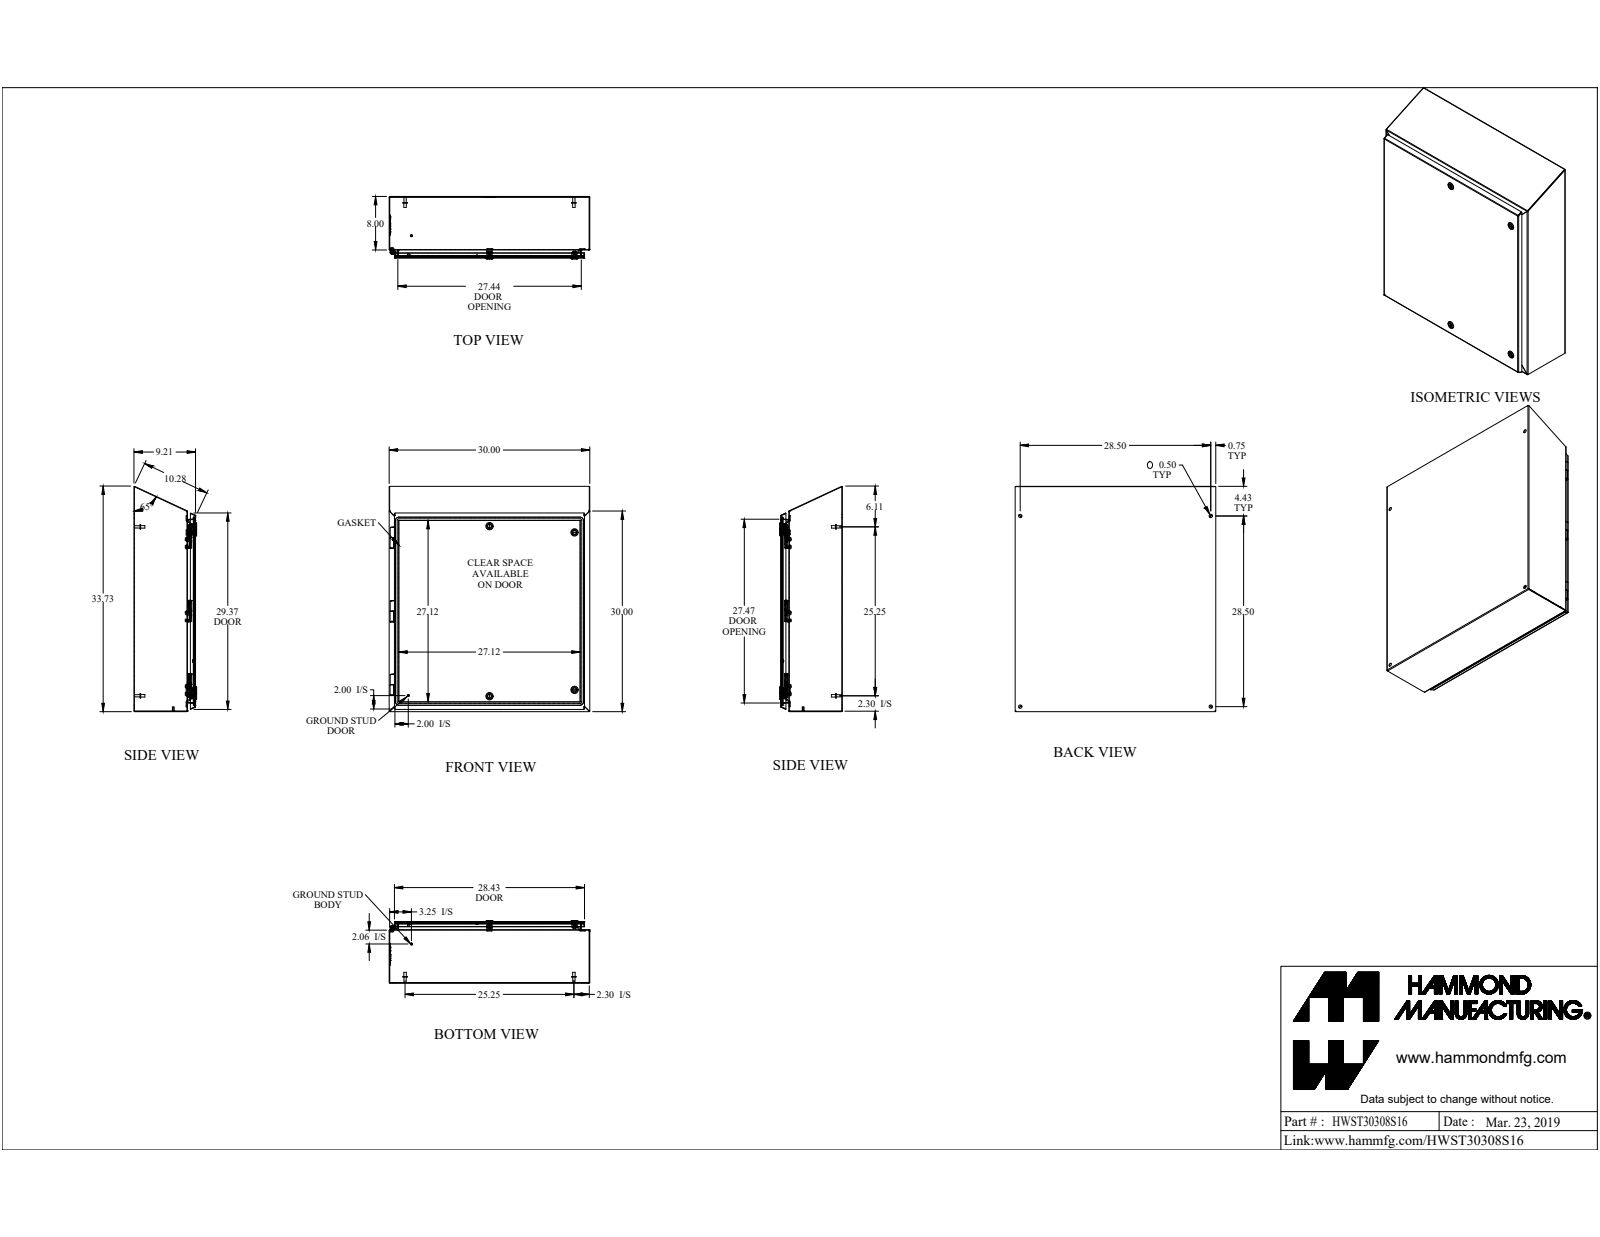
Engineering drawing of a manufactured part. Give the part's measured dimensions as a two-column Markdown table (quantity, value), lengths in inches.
| quantity | value |
| --- | --- |
| part name | HWST30308S16 |
| STEP written by | SolidWorks 2019 (AUTOMOTIVE_DESIGN) |
| units | inches |
| bodies | 62 solids, 1442 faces (901 planar, 401 cylindrical, 140 other) |
| overall size | 33.684 × 30 × 9.37 |
| volume | 253 in³ |
| surface area | 6 871 in² |
| round holes (diameter × count) | 0.5 × 8, 0.194 × 6, 0.194 × 6, 0.24 × 6, 0.275 × 6, 0.197 × 4, 0.387 × 4, 0.63 × 4, 0.768 × 4, 0.13 × 2, 0.24 × 1, 3.5 × 1 |
| round bosses / shafts (diameter × count) | 0.226 × 12, 0.625 × 10, 0.236 × 5, 1.1 × 4, 0.785 × 4, 0.65 × 4, 0.525 × 4, 0.375 × 4 |
| partial cylindrical surfaces (radius × count) | 0.039 × 24, 0.25 × 24, 0.125 × 20, 0.012 × 16, 0.108 × 16, 0.03 × 14, 0.036 × 12, 0.108 × 9 |
| main face-to-face distances | 0.072, 9.066, 9.138, 0.072, 9.138, 9.21, 29.928, 7.928, 29.856, 30 |
| hole center spacings | 1.142, 10.99, 10.989, 21.979, 28.5, 9.848, 12.131, 9.847 |
